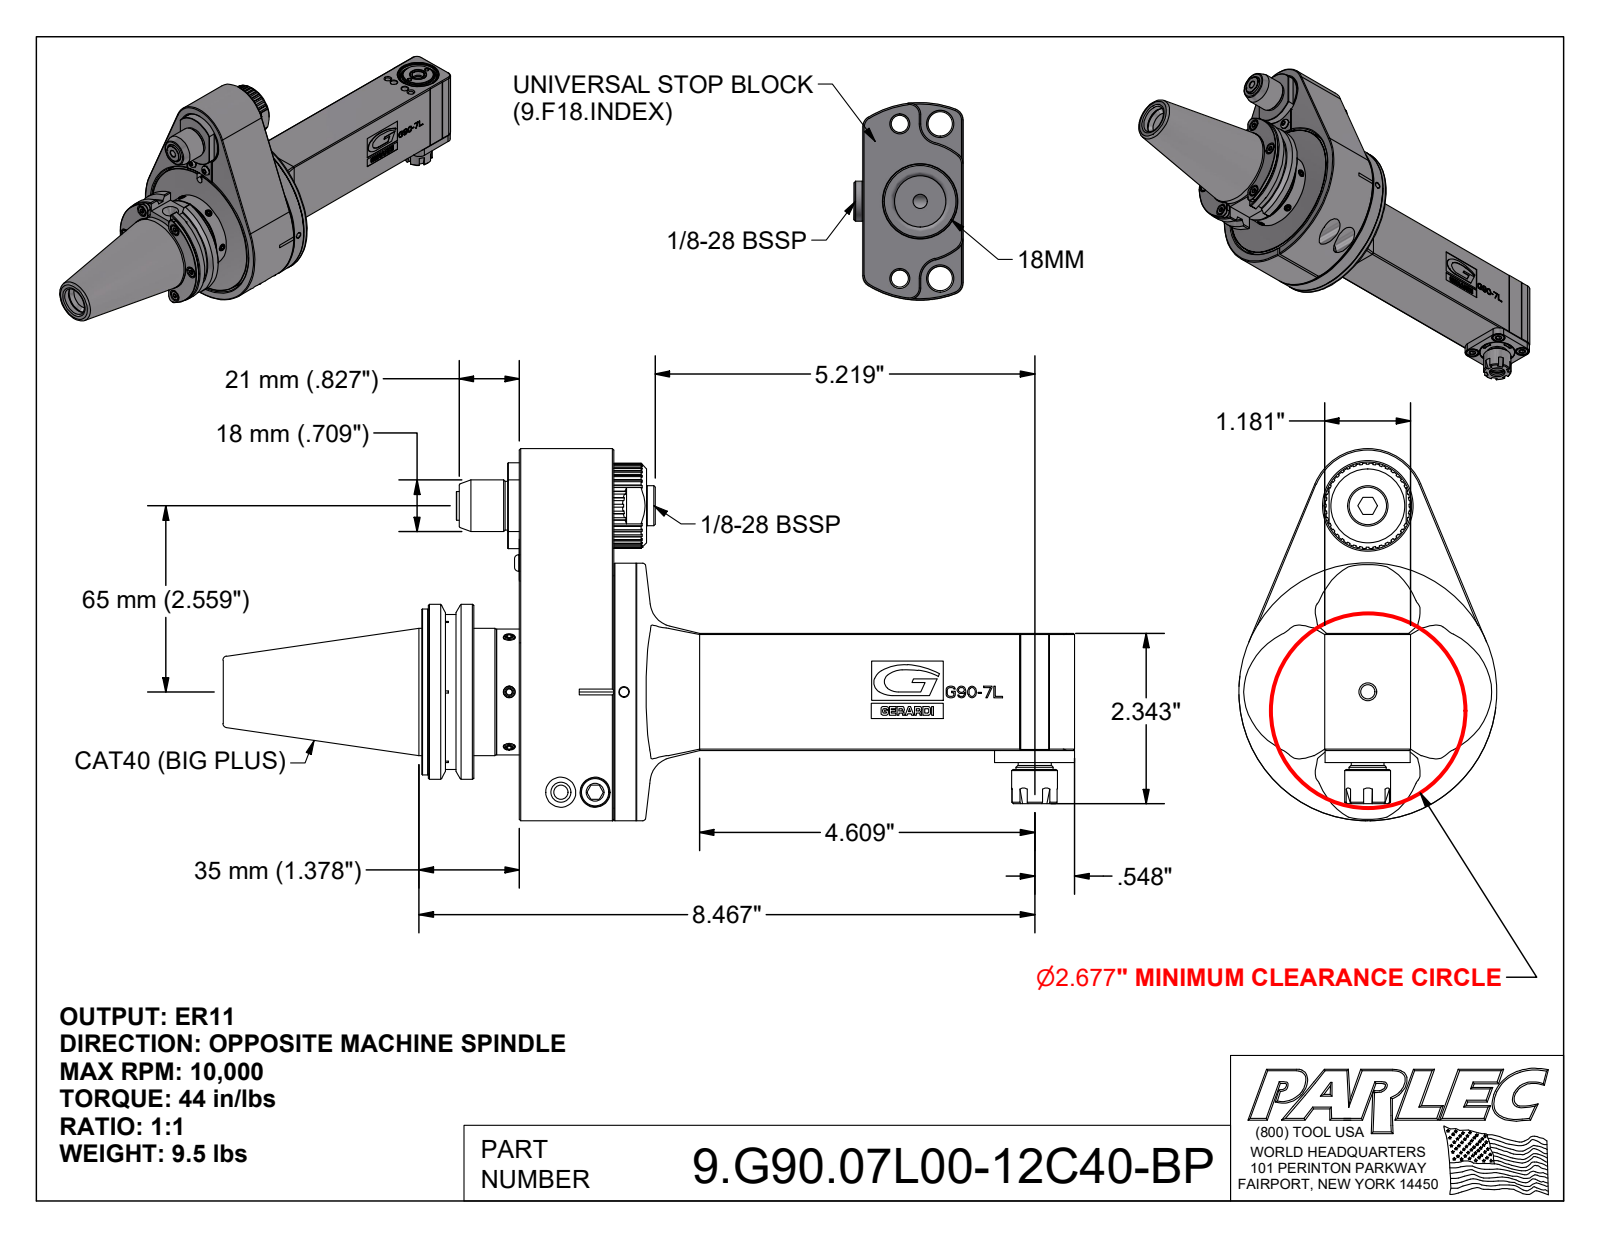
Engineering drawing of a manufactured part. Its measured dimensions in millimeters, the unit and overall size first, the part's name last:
Units: millimetres
Overall size (bounding box): 297.4 × 130 × 90
Round holes (diameter × count): ⌀3.3 ×10, ⌀2.5 ×6, ⌀7.5 ×5, ⌀4 ×4, ⌀4.2 ×4, ⌀5 ×4, ⌀7 ×3, ⌀2.1 ×2, ⌀10.5 ×2, ⌀5.5 ×1, ⌀6.1 ×1, ⌀8.5 ×1
Round bosses / shafts (diameter × count): ⌀5.8 ×6, ⌀3 ×6, ⌀7 ×5, ⌀10 ×4, ⌀4 ×3, ⌀30 ×2, ⌀9 ×2, ⌀5.7 ×2
Partial cylindrical surfaces — rounded edges, fillets, slot ends (radius × count): R3 ×9, R0.75 ×8, R4 ×4, R4.25 ×4, R9 ×4, R1.5 ×3, R2 ×2, R2.15 ×2
Main face-to-face distances: 30, 41, 3, 33, 8.5, 5.5, 24.5, 7, 37, 1
Hole centre spacings: 27, 46.76, 11.1, 14.51, 19.9, 14, 54, 5
Volume: 590 217 mm³ · Surface area: 137 961 mm²
Bodies: 3 solids, 1410 faces (803 planar, 262 cylindrical, 345 other)
Part name (STEP PRODUCT): 9.G90.07L00-12C40-BP
STEP written by: Autodesk Inventor 2022 (AUTOMOTIVE_DESIGN)
